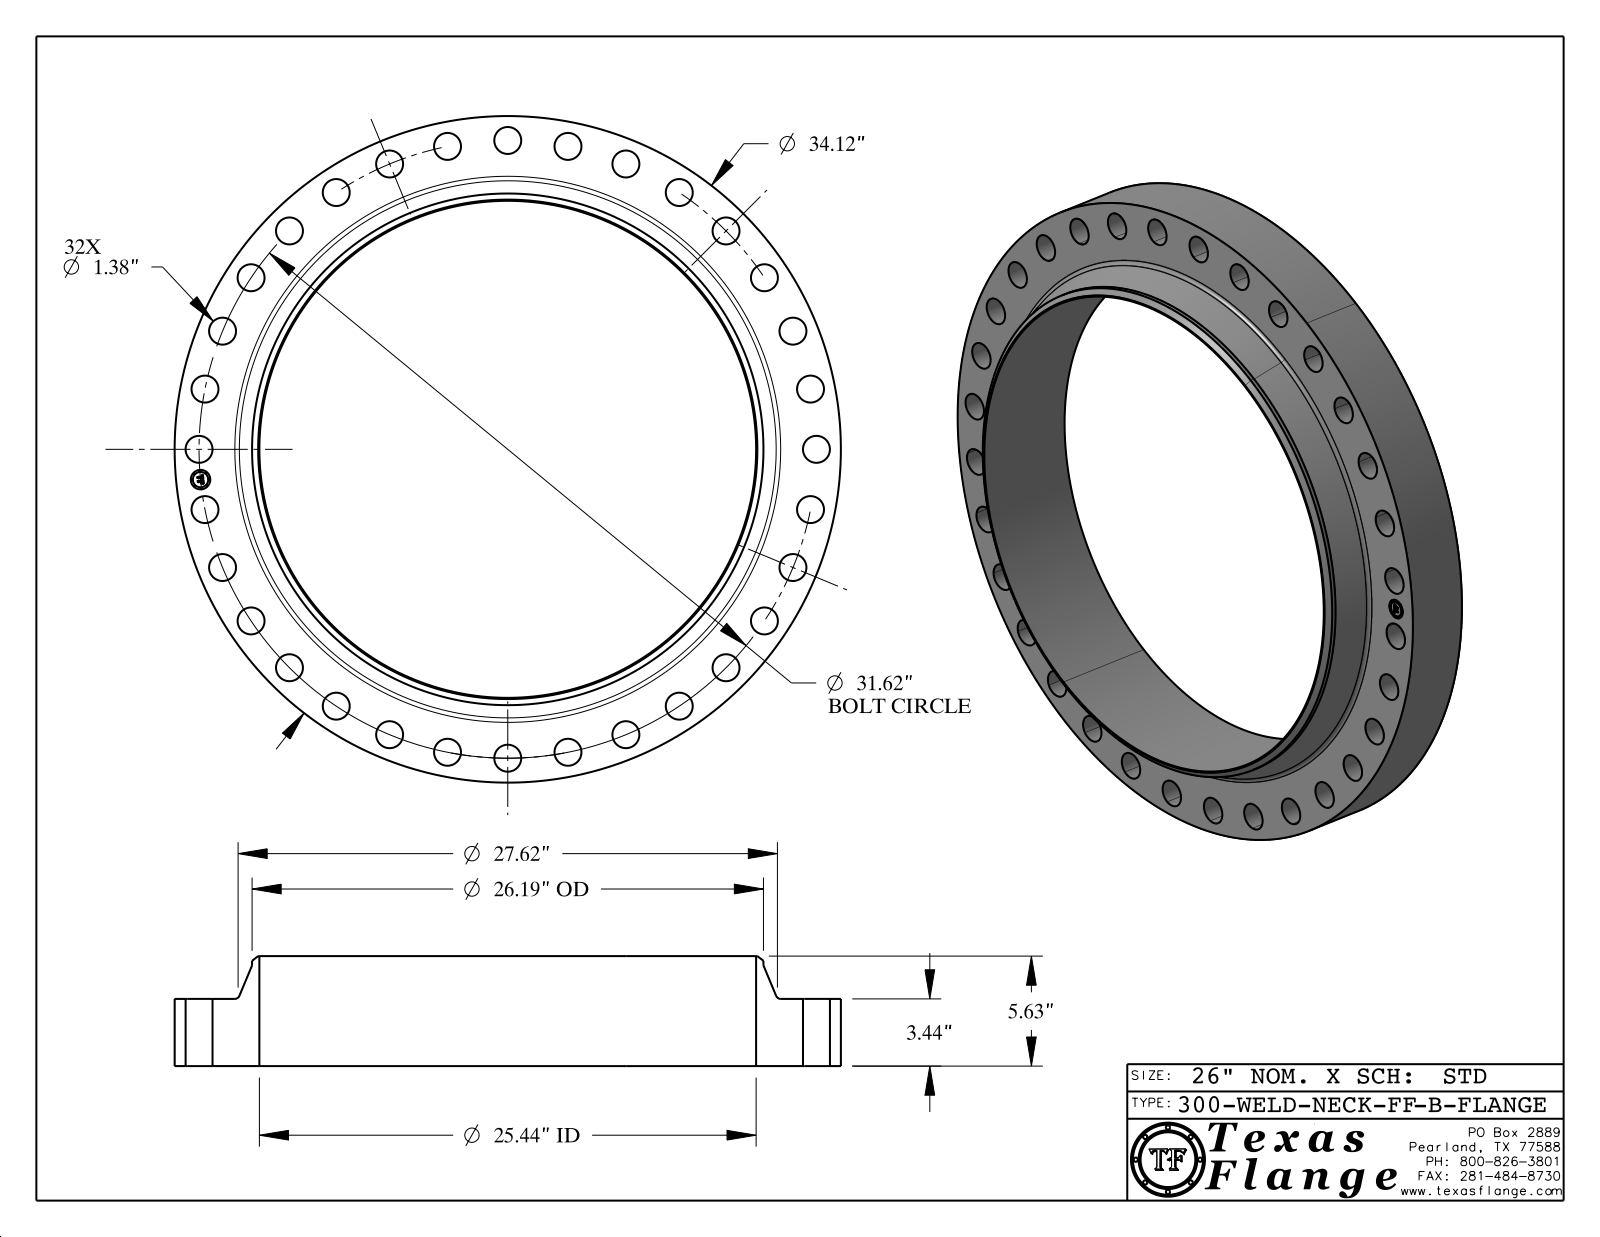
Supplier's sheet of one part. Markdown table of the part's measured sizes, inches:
| quantity | value |
| --- | --- |
| part name | 300-WELD-NECK-FF, Series B |
| STEP written by | CATIA V5 STEP AP214 (AUTOMOTIVE_DESIGN) |
| units | inches |
| bodies | 1 solid, 464 faces (368 planar, 90 cylindrical, 6 other) |
| overall size | 34.12 × 34.12 × 5.63 |
| volume | 1 347 in³ |
| surface area | 2 132 in² |
| round holes (diameter × count) | 1.38 × 32, 1 × 1, 25.44 × 1 |
| round bosses / shafts (diameter × count) | 0.061 × 8, 34.12 × 1, 26.19 × 1, 0.788 × 1 |
| main face-to-face distances | 3.44, 5.63, 2.19, 3.425, 0.015, 2.205, 0.298, 0.293, 0.054, 0.193 |
| hole center spacings | 15.81, 6.169, 26.291, 31.468, 14.906, 27.887, 30.259, 20.059 |
